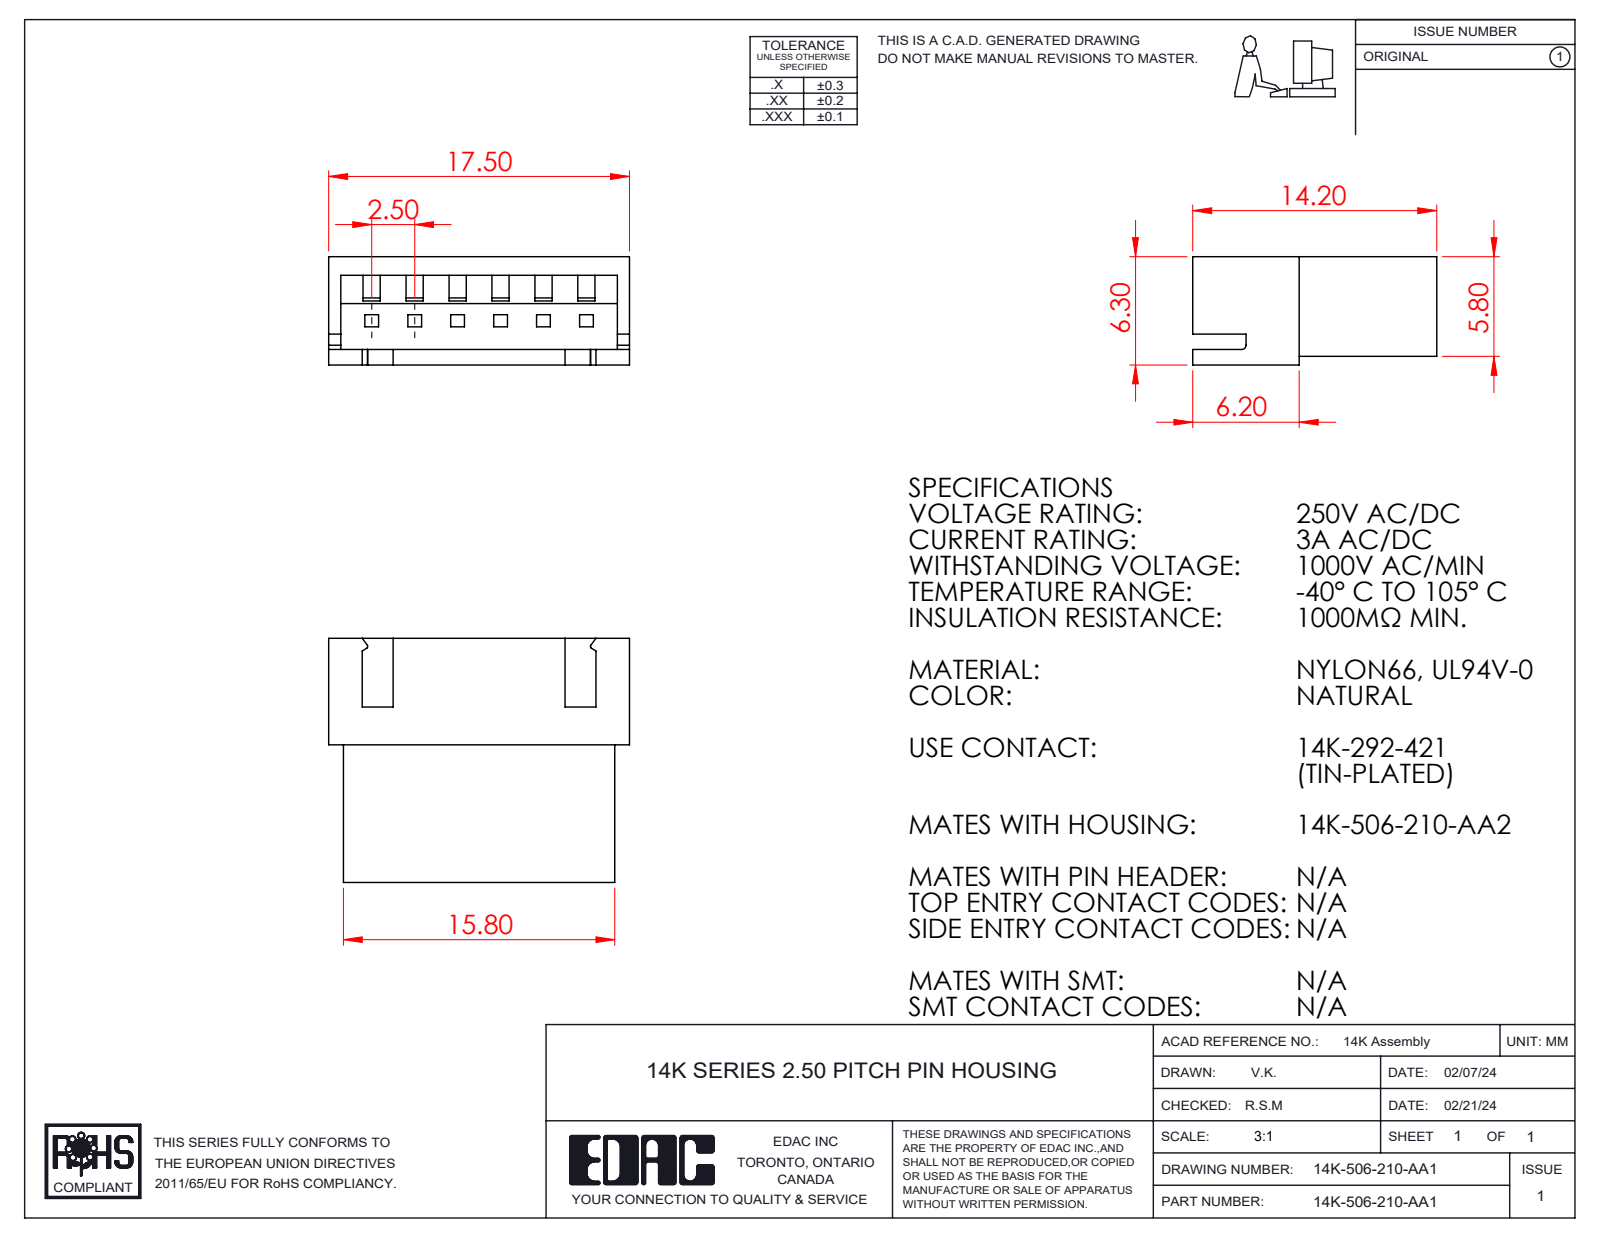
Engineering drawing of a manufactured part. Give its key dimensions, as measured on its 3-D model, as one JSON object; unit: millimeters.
{"part_name": "14K-506-210-AA1", "step_written_by": "SolidWorks 2023 (CONFIG_CONTROL_DESIGN)", "units": "millimeters", "bodies": {"solids": 1, "faces": 189, "planar": 185, "cylindrical": 4, "other": 0}, "overall_size": [17.5, 14.2, 6.3], "volume_mm3": 744, "surface_area_mm2": 1710, "partial_cylinders_radius": [[0.1, 2], [0.25, 1]], "face_to_face_distances": [0.5, 2.5, 5, 5.8, 0.9, 3, 2, 7.5, 4.5, 1.5]}
